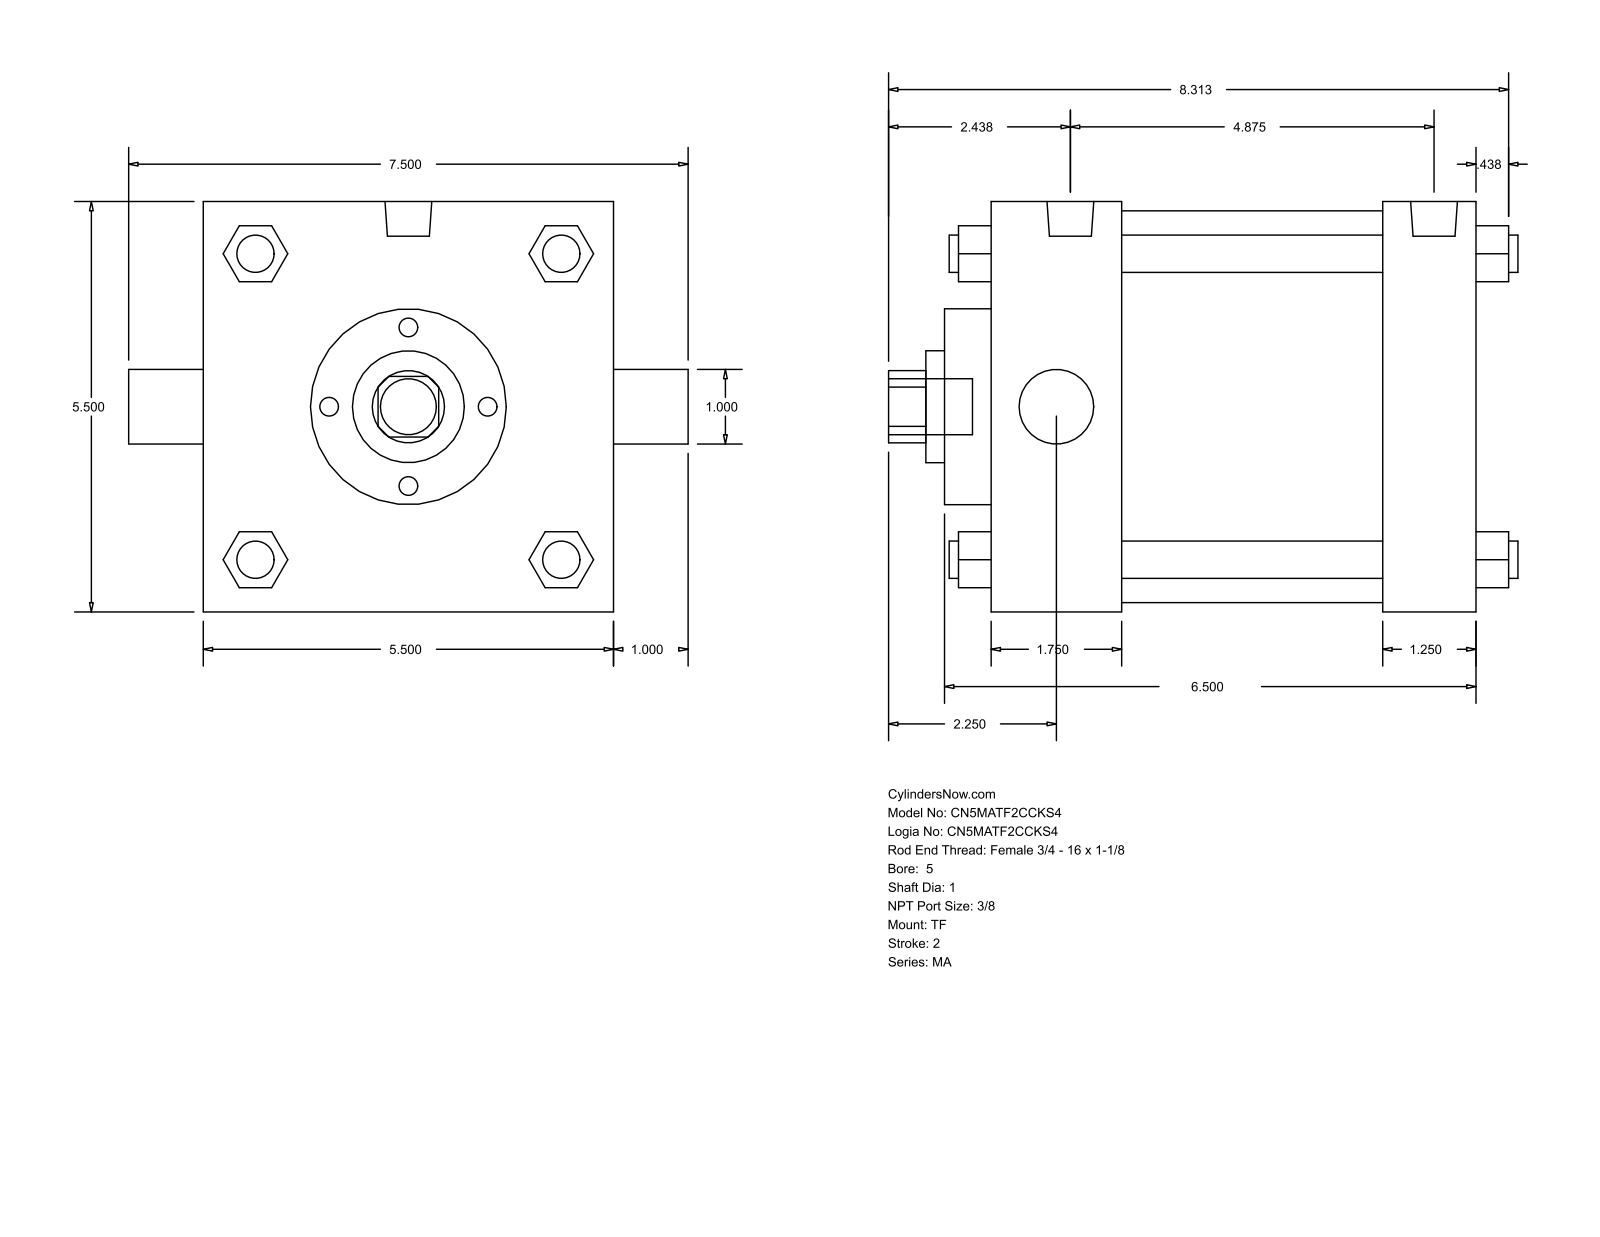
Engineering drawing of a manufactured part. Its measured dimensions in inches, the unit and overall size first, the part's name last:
Units: inches
Overall size (bounding box): 8.437 × 7.5 × 5.5
Round holes (diameter × count): ⌀1 ×2, ⌀1.5 ×1, ⌀2.625 ×1, ⌀5.25 ×1
Round bosses / shafts (diameter × count): ⌀0.5 ×4, ⌀0.437 ×3, ⌀0.627 ×2, ⌀0.75 ×1
Partial cylindrical surfaces — rounded edges, fillets, slot ends (radius × count): R0.484 ×1
Main face-to-face distances: 5.5, 6.5, 5.25, 1.25, 1.75, 3.5, 4.75, 0.625, 2.375, 5.875
Bodies: 0 solids, 122 faces (93 planar, 29 cylindrical, 0 other)
Part name (STEP PRODUCT): MA_TF__0500_1
STEP written by: GSSL Pune (CONFIG_CONTROL_DESIGN)
